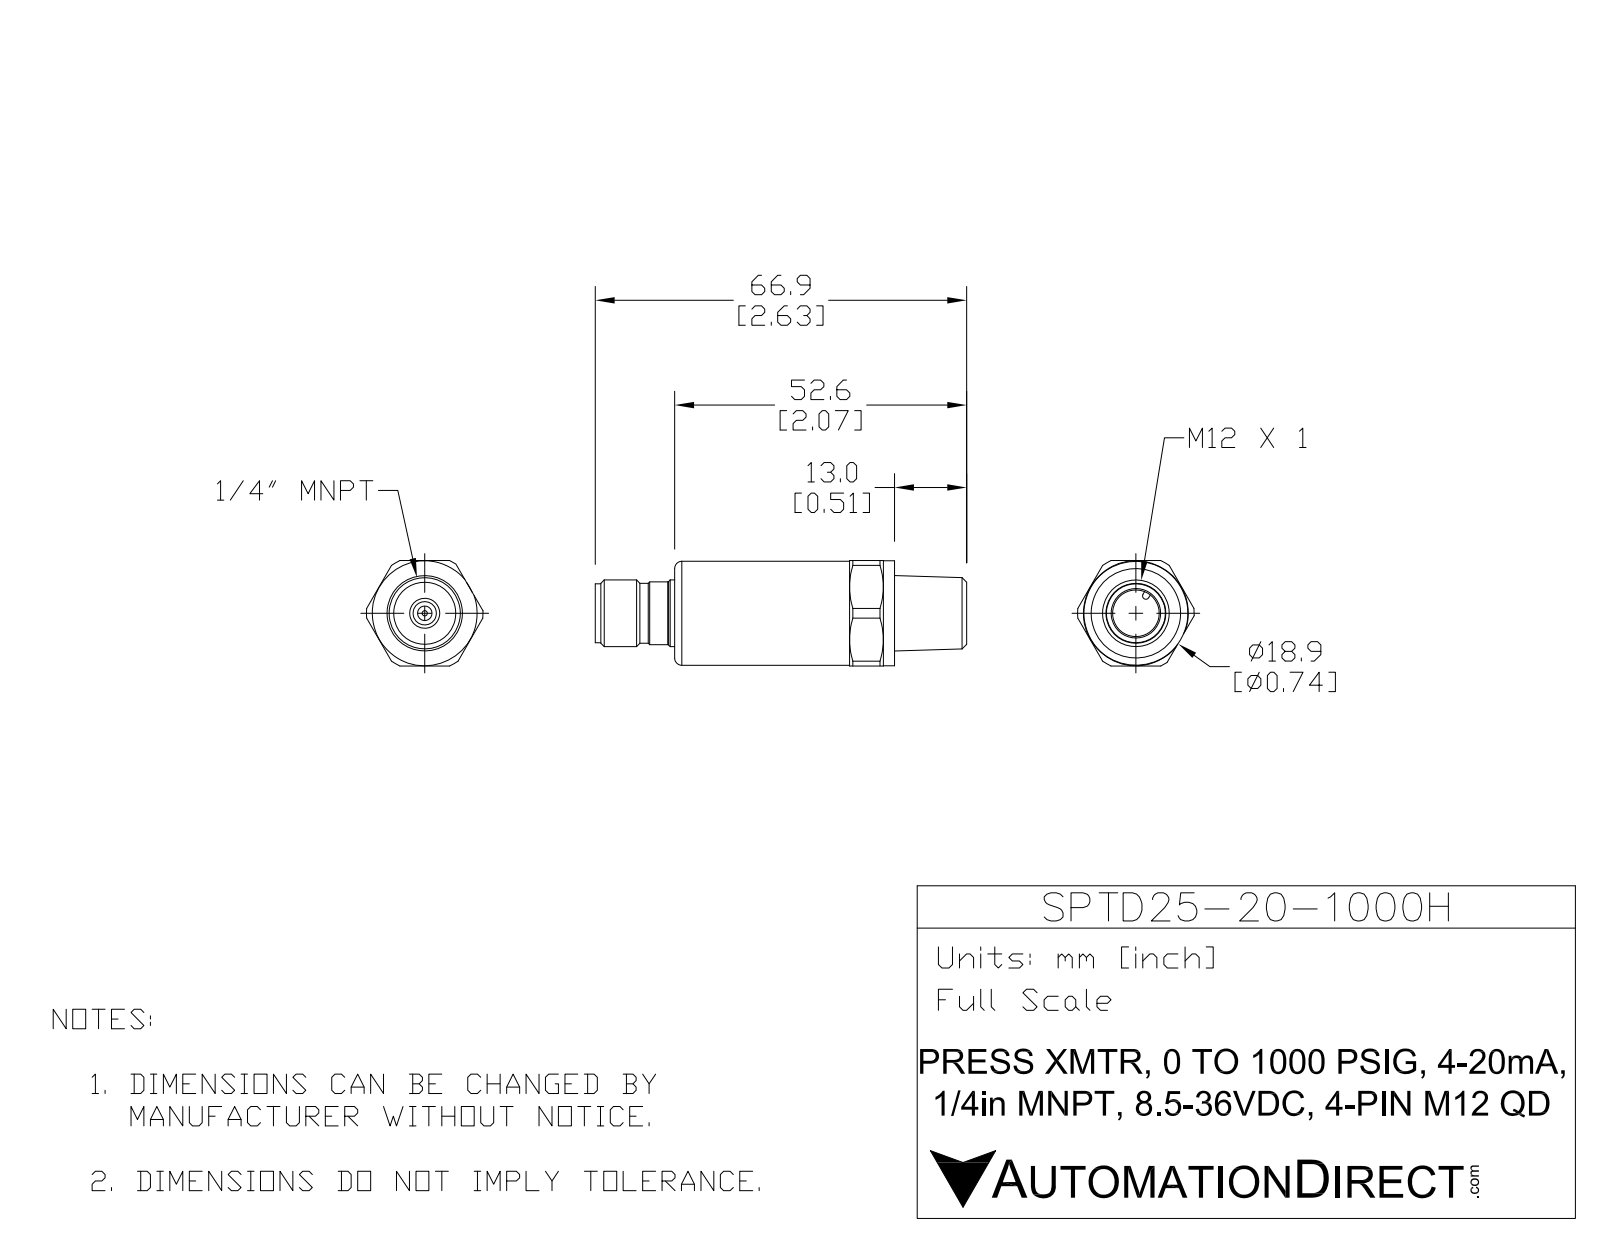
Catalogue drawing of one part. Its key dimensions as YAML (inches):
part_name: "SPDT25-20-1000H"
step_written_by: "SolidWorks 2015 (AUTOMOTIVE_DESIGN)"
units: inches
bodies: {solids: 7, faces: 177, planar: 44, cylindrical: 53, other: 80}
overall_size: [2.634, 0.849, 0.744]
volume: 0.821
surface_area: 8.272
round_holes:
  - {diameter: 0.165, count: 1}
  - {diameter: 0.331, count: 1}
  - {diameter: 0.654, count: 1}
round_bosses_or_shafts:
  - {diameter: 0.055, count: 4}
  - {diameter: 0.039, count: 4}
  - {diameter: 0.744, count: 1}
  - {diameter: 0.472, count: 1}
  - {diameter: 0.445, count: 1}
  - {diameter: 0.425, count: 1}
  - {diameter: 0.417, count: 1}
  - {diameter: 0.413, count: 1}
partial_cylinders:
  - {radius: 0.024, count: 1}
face_to_face_distances: [0.744, 2.069, 0.515, 1.554, 2.287, 1.772, 0.219, 0.563, 0.047, 1.506]
